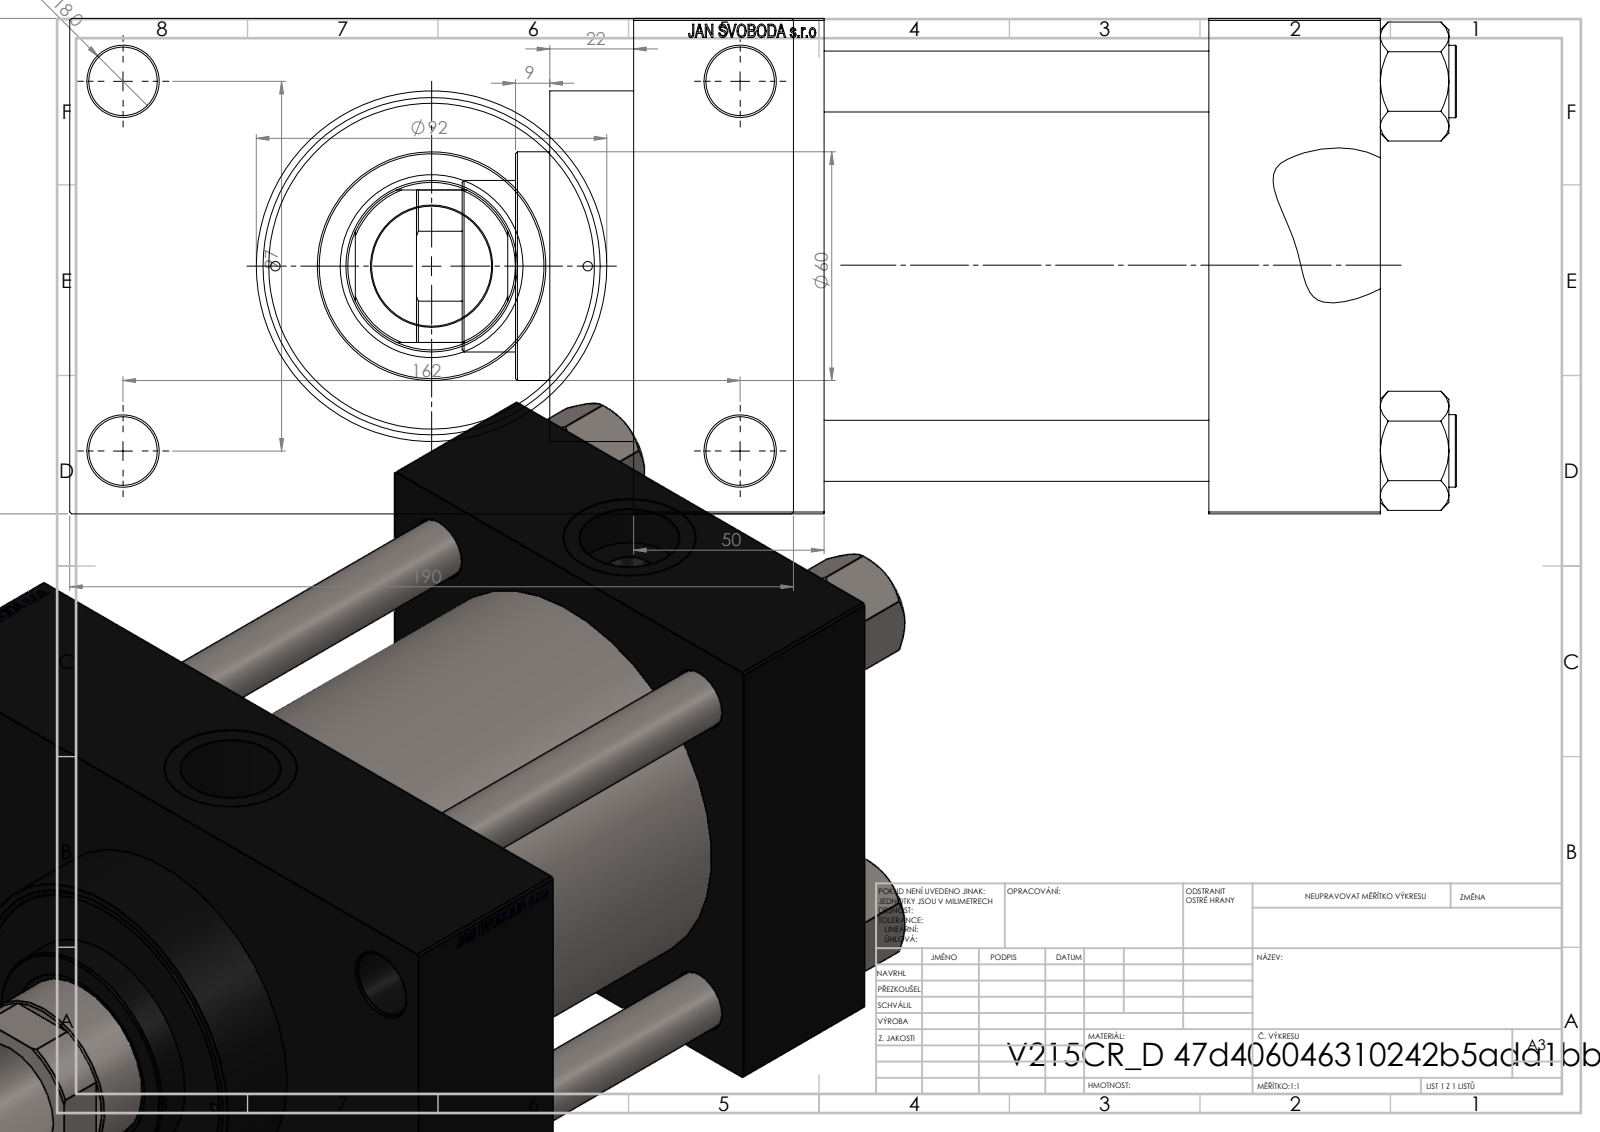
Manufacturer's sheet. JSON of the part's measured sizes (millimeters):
{"part_name": "V215CR_D_Body; NUT_M5_D; V215_VC_A; V215CR_D_TYCINKA (+1 more)", "step_written_by": "SolidWorks 2019 (CONFIG_CONTROL_DESIGN)", "units": "millimeters", "bodies": {"solids": 11, "faces": 1160, "planar": 547, "cylindrical": 93, "other": 520}, "overall_size": [273, 190, 130], "volume_mm3": 2707000, "surface_area_mm2": 381927, "round_holes": [[16, 4], [18, 4], [2.5, 2], [7, 2], [26.44, 2], [35, 2], [31.5, 1], [45, 1], [48, 1], [76, 1], [85.5, 1], [100, 1]], "round_bosses_or_shafts": [[19, 4], [106, 1], [92, 1], [60, 1]], "partial_cylinders_radius": [[22, 1]], "face_to_face_distances": [50, 130, 45, 146, 101, 196, 151, 30, 160, 190], "hole_center_spacings": [32.55, 49.02, 62.87, 68.52, 94.41, 96.9, 101.73, 102.27]}
